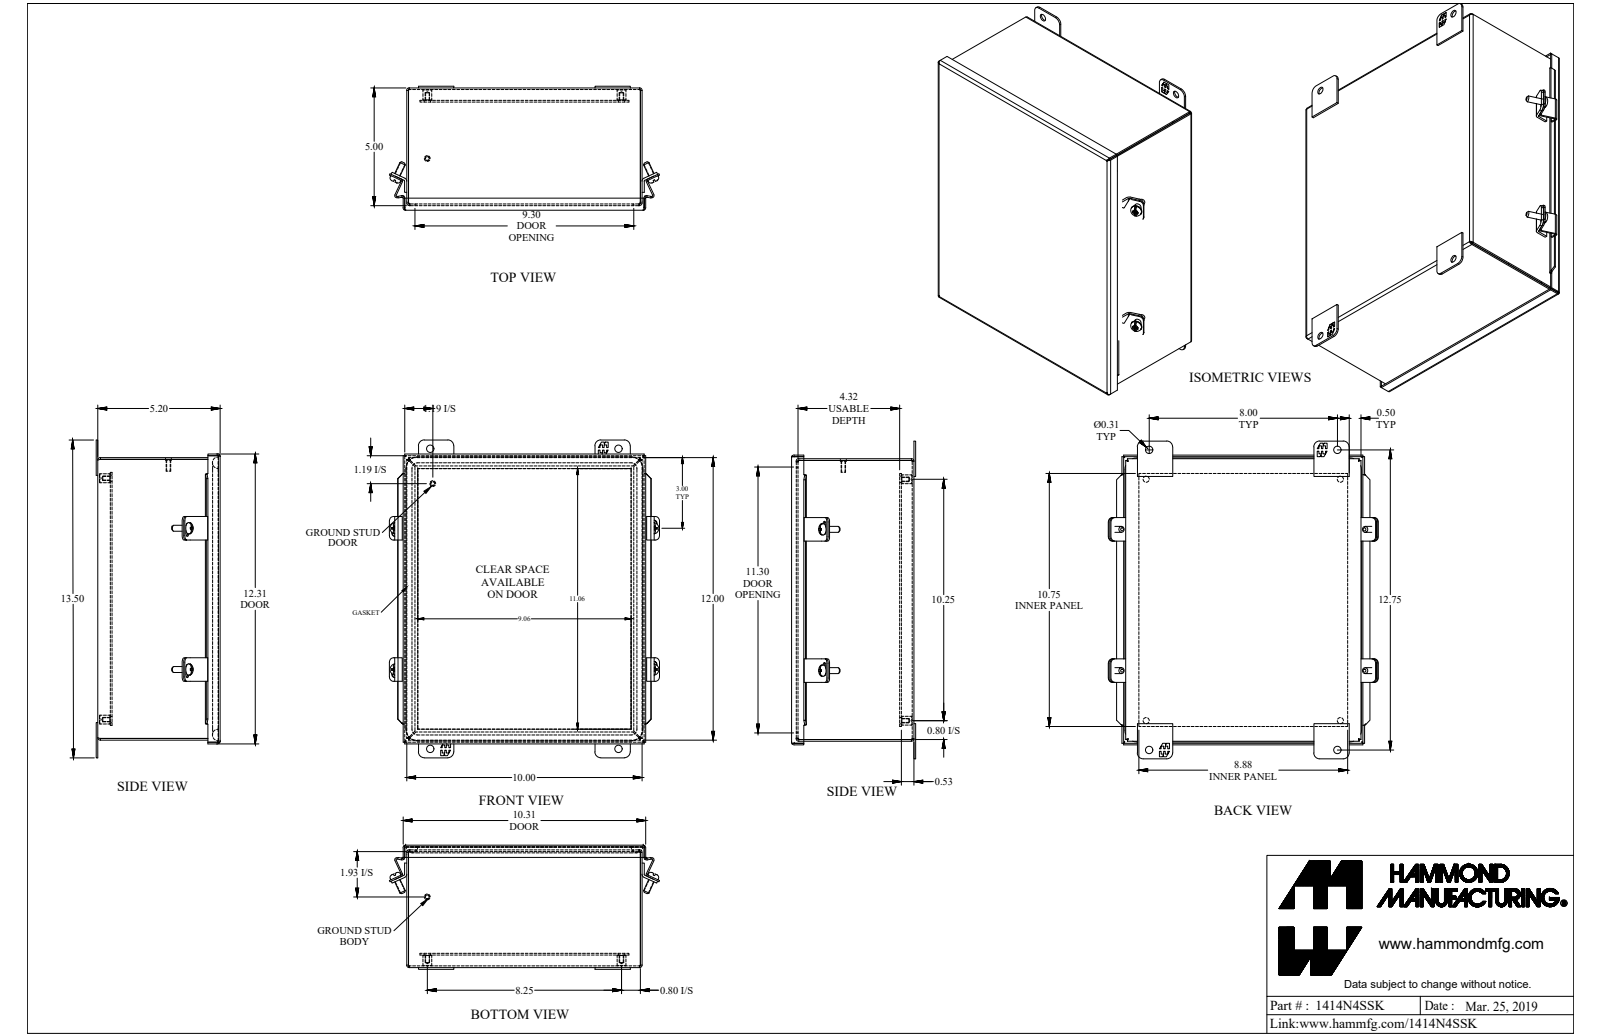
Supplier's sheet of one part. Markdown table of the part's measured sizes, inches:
| quantity | value |
| --- | --- |
| part name | 1414N4SSK |
| STEP written by | SolidWorks 2018 (AUTOMOTIVE_DESIGN) |
| units | inches |
| bodies | 26 solids, 717 faces (473 planar, 168 cylindrical, 76 other) |
| overall size | 13.5 × 11.475 × 5.269 |
| volume | 48.35 in³ |
| surface area | 1 340 in² |
| round holes (diameter × count) | 0.156 × 4, 0.213 × 4, 0.265 × 4, 0.313 × 4 |
| round bosses / shafts (diameter × count) | 0.25 × 6, 0.48 × 4, 0.375 × 4, 0.19 × 2 |
| partial cylindrical surfaces (radius × count) | 0.25 × 24, 0.188 × 16, 0.036 × 10, 0.108 × 10, 0.141 × 8, 0.007 × 4, 0.01 × 4, 0.029 × 4 |
| main face-to-face distances | 0.072, 5.125, 4.593, 0.532, 5.197, 5.053, 9.928, 0.604, 4.665, 0.46 |
| hole center spacings | 8.22, 8.25, 14.081, 1.256, 11.501, 1.256, 6, 8 |
